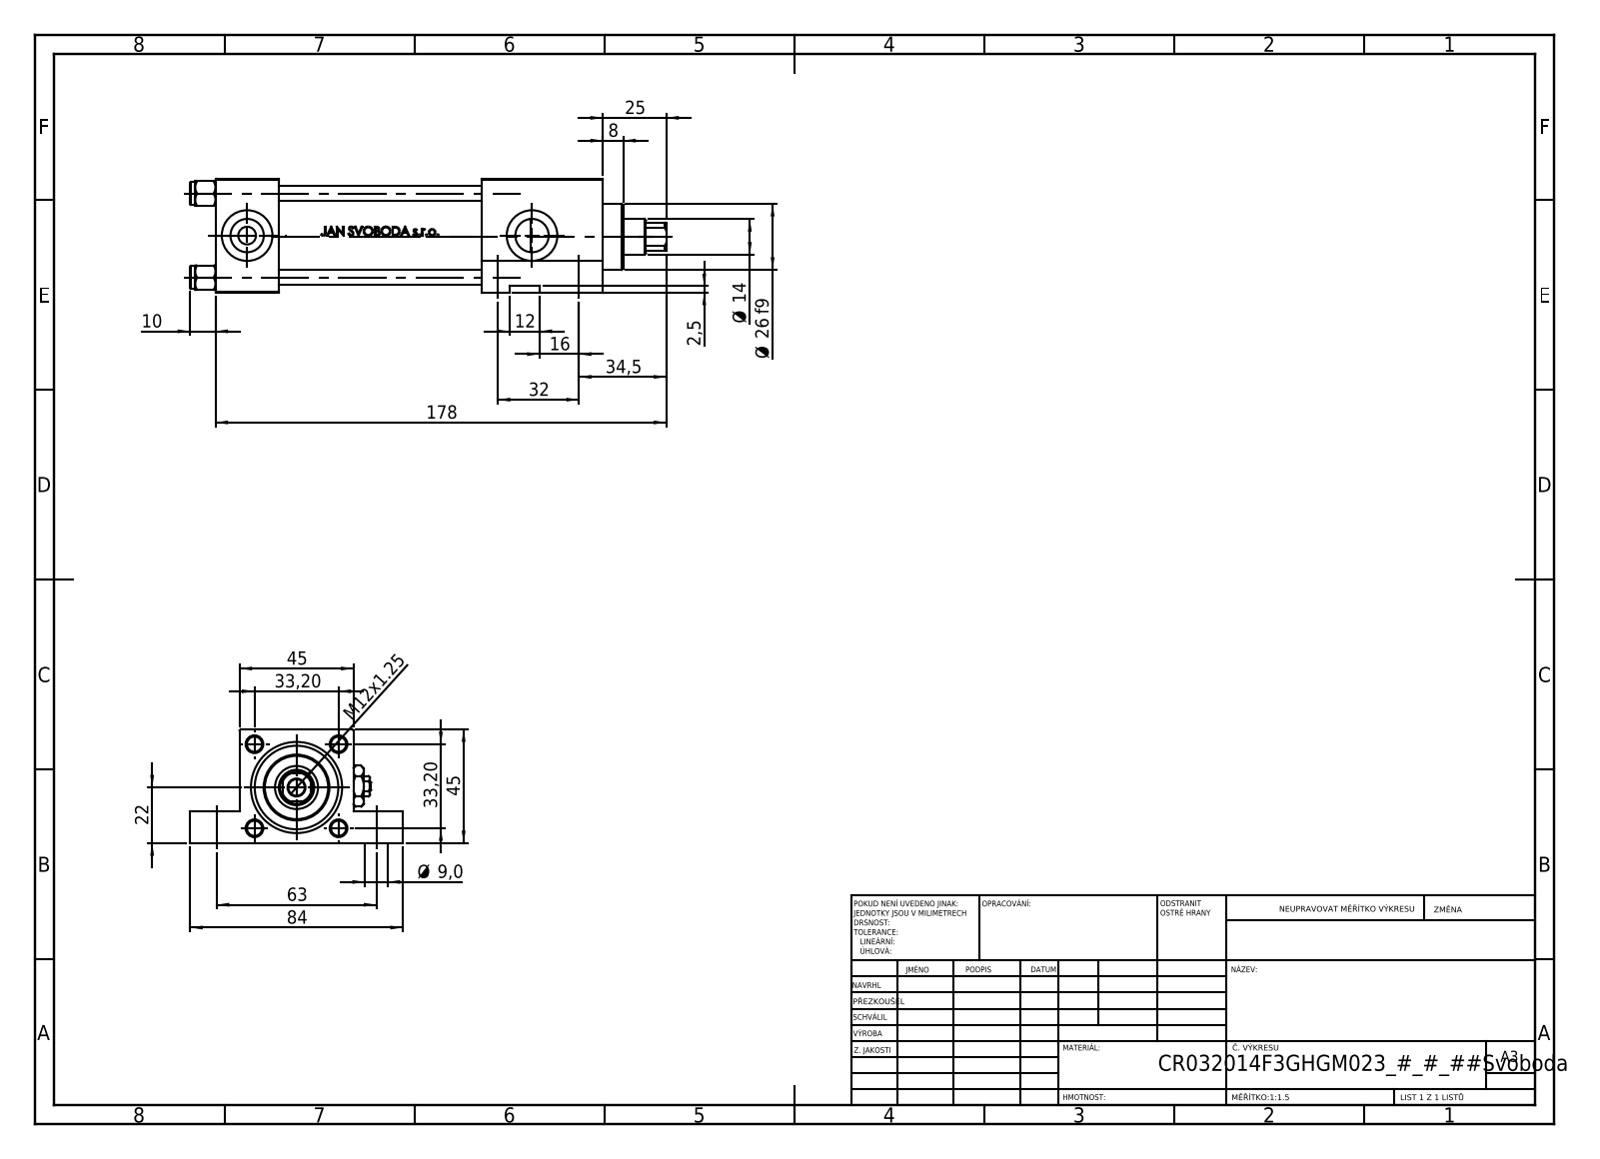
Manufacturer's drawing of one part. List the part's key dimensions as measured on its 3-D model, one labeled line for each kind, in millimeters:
Part name (STEP PRODUCT): V215_VC_A; V215CR_F_TYCINKA; V215CR_F_Body; NUT_M5_F (+2 more)
STEP written by: SolidWorks 2019 (CONFIG_CONTROL_DESIGN)
Units: millimetres
Bodies: 13 solids, 1198 faces (482 planar, 134 cylindrical, 582 other)
Overall size (bounding box): 188 × 84 × 45
Volume: 228 299 mm³ · Surface area: 84 666 mm²
Round holes (diameter × count): ⌀6 ×4, ⌀13.16 ×3, ⌀20 ×3, ⌀7 ×2, ⌀9 ×2, ⌀9 ×2, ⌀6.5 ×1, ⌀13 ×1, ⌀14 ×1, ⌀17 ×1, ⌀24 ×1, ⌀32 ×1
Round bosses / shafts (diameter × count): ⌀9 ×4, ⌀38 ×1, ⌀26 ×1
Partial cylindrical surfaces — rounded edges, fillets, slot ends (radius × count): R6.5 ×1
Main face-to-face distances: 45, 25, 128, 153, 32.5, 105, 80, 48, 12.5, 10
Hole centre spacings: 33.2, 23.13, 23.83, 32, 46.95, 63, 70.66, 7
